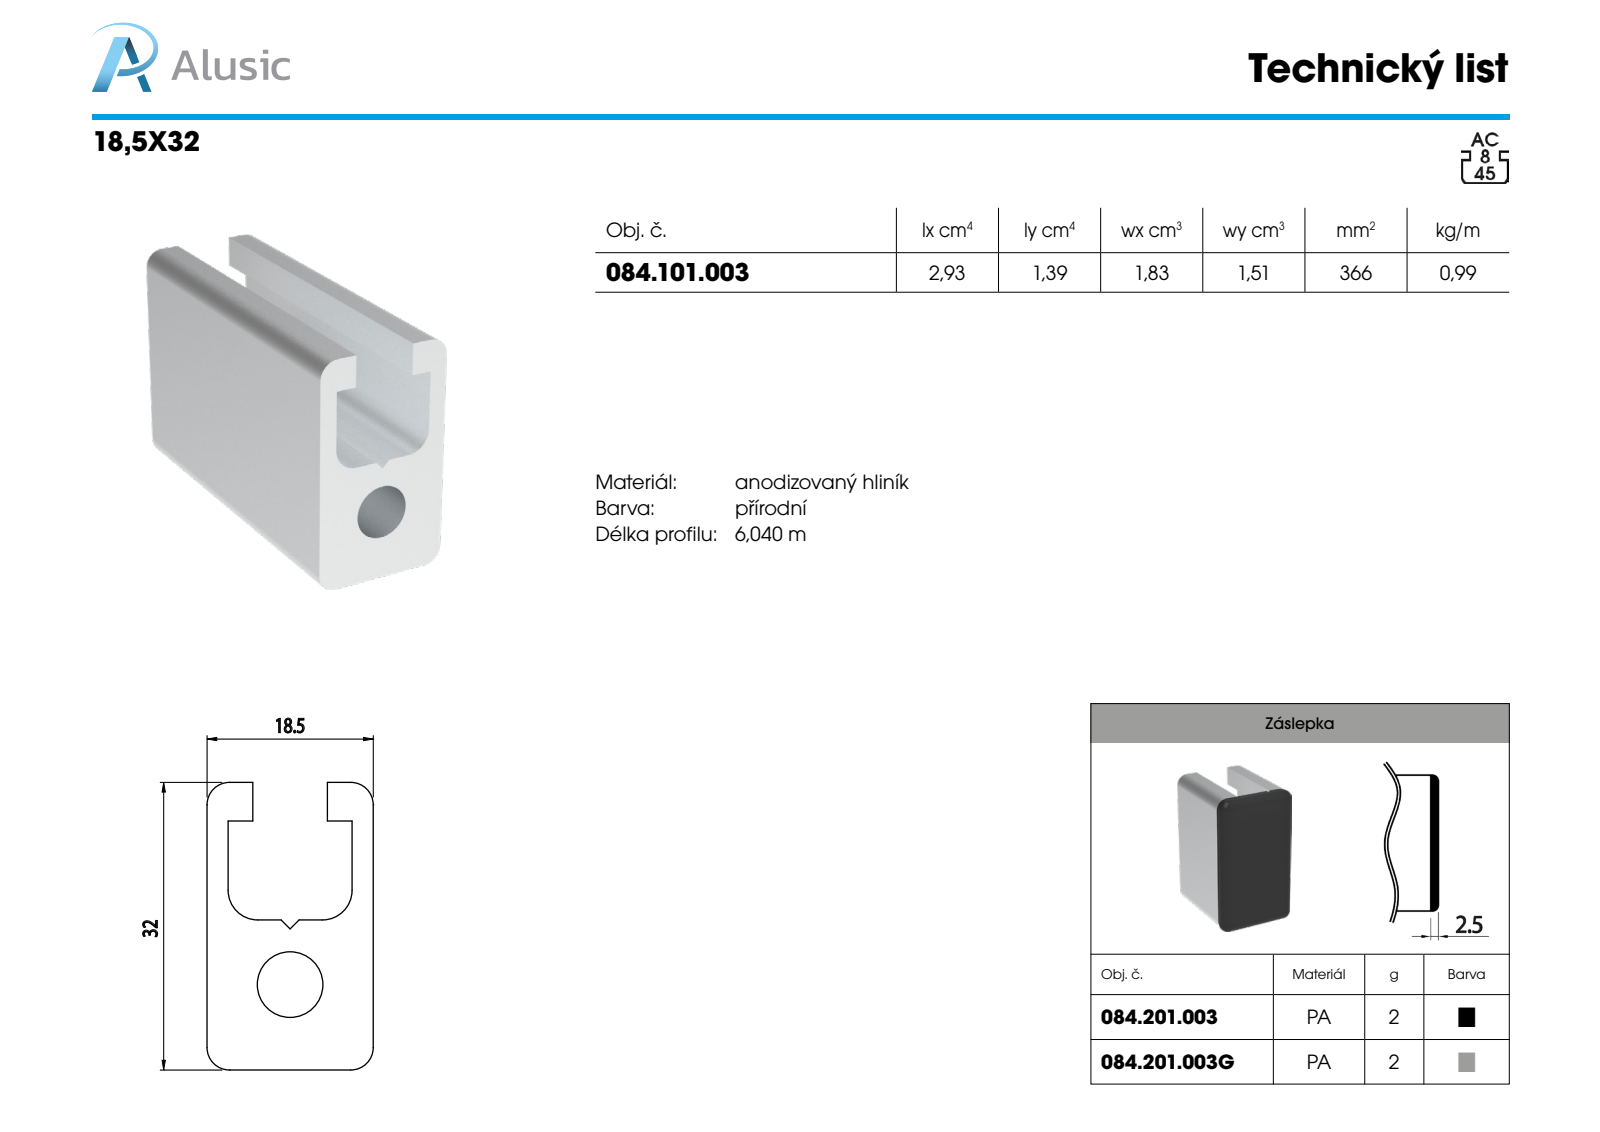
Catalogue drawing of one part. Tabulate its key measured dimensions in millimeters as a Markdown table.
| quantity | value |
| --- | --- |
| part name | 084.201.003-1 |
| STEP written by | SolidWorks 2011 (CONFIG_CONTROL_DESIGN) |
| units | millimeters |
| bodies | 1 solid, 74 faces (18 planar, 20 cylindrical, 36 other) |
| overall size | 32 × 18.5 × 7.3 |
| volume | 1 527 mm³ |
| surface area | 1 567 mm² |
| round holes (diameter × count) | 6 × 1 |
| round bosses / shafts (diameter × count) | 7.5 × 1 |
| partial cylindrical surfaces (radius × count) | 0.5 × 8, 2 × 8 |
| main face-to-face distances | 2.5, 3, 0.5, 18.5, 3.7, 1.2, 0.7, 32, 7.3, 4.8 |
